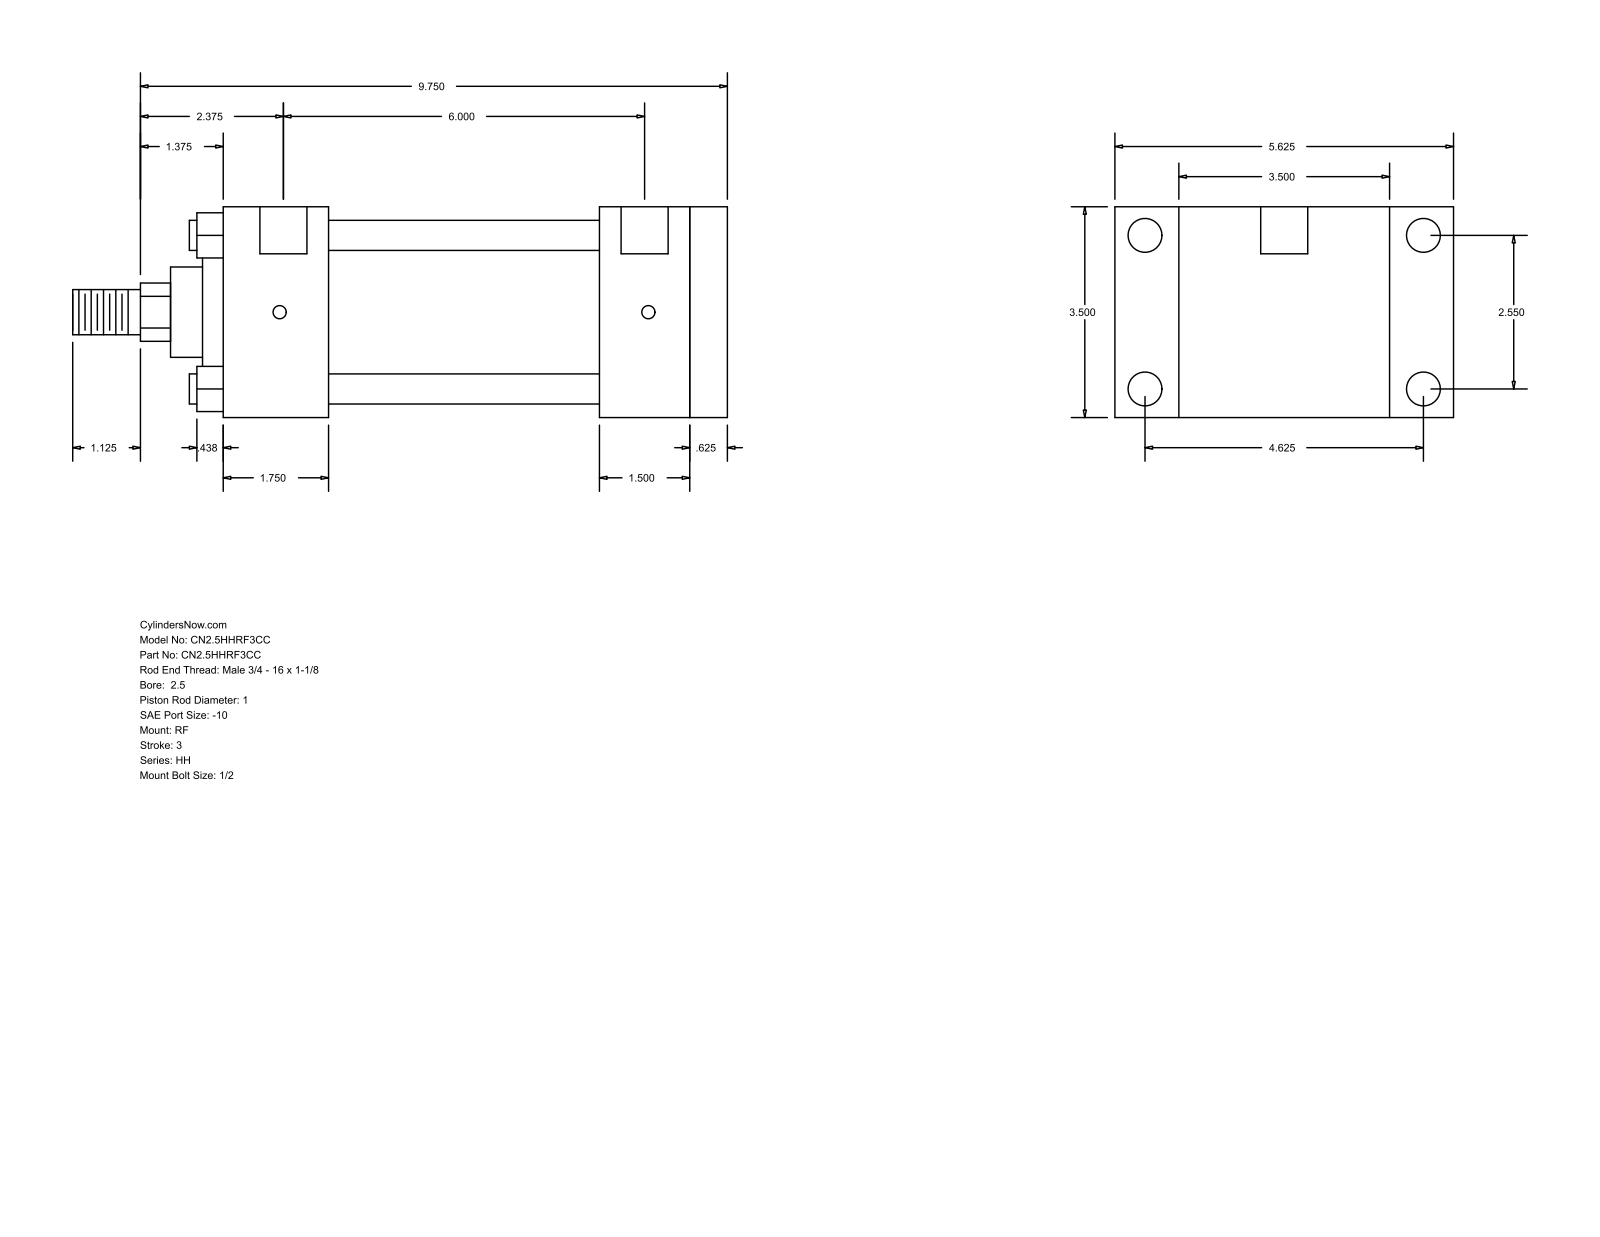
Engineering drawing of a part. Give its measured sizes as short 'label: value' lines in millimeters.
name: HH_RF__0250_1
written by: GSSL Pune (CONFIG_CONTROL_DESIGN)
unit: mm
bodies: 0 solids, 94 faces (65 planar, 29 cylindrical, 0 other)
size: 276.23 × 142.88 × 88.9
holes: 4× ⌀5.56, 4× ⌀14.3, 2× ⌀19.84
bosses: 4× ⌀12.7, 1× ⌀73.03, 1× ⌀60.33, 1× ⌀38.1, 1× ⌀25.4, 1× ⌀19.05
rounds: 1× R12.29
face distances: 88.9, 15.87, 196.86, 212.73, 38.1, 44.46, 152.4, 168.27, 158.76, 114.3
hole spacings: 1.59, 64.76, 117.48, 134.15, 153.98, 155.57, 152.39
